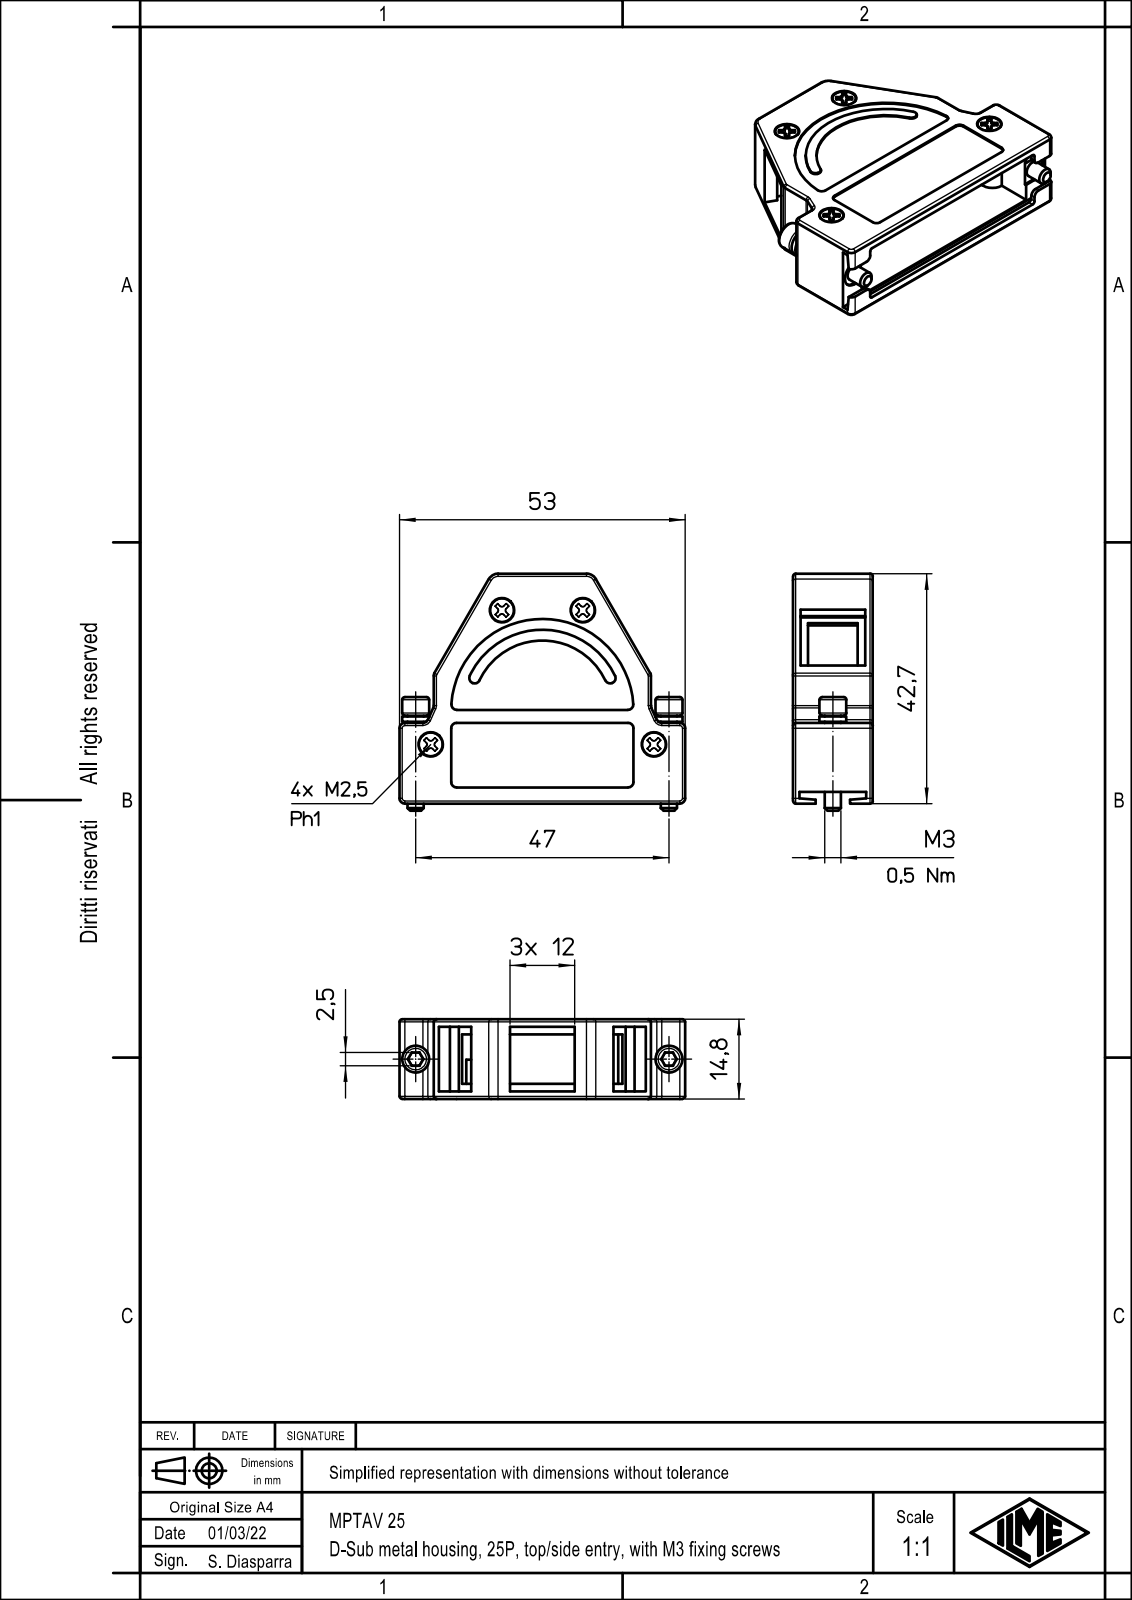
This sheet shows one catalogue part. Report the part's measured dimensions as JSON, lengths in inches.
{"part_name": "MPTAV_25", "step_written_by": "Creo Elements/Direct Modeling 20.1B 02-Apr-2019 (C) Parametric Technology GmbH (AUTOMOTIVE_DESIGN)", "units": "inches", "bodies": {"solids": 1, "faces": 722, "planar": 169, "cylindrical": 213, "other": 340}, "overall_size": [2.087, 1.732, 0.583], "volume_in3": 0.543, "surface_area_in2": 15.28, "round_bosses_or_shafts": [[0.197, 2], [0.118, 2]], "partial_cylinders_radius": [[0.02, 42], [0.039, 22], [0.079, 3], [0.031, 2], [0.096, 2], [0.508, 1], [0.587, 1], [0.665, 1]], "face_to_face_distances": [0.051, 0.516, 0.059, 0.524, 0.575, 0.465, 0.567, 0.583, 0.047, 0.055]}
